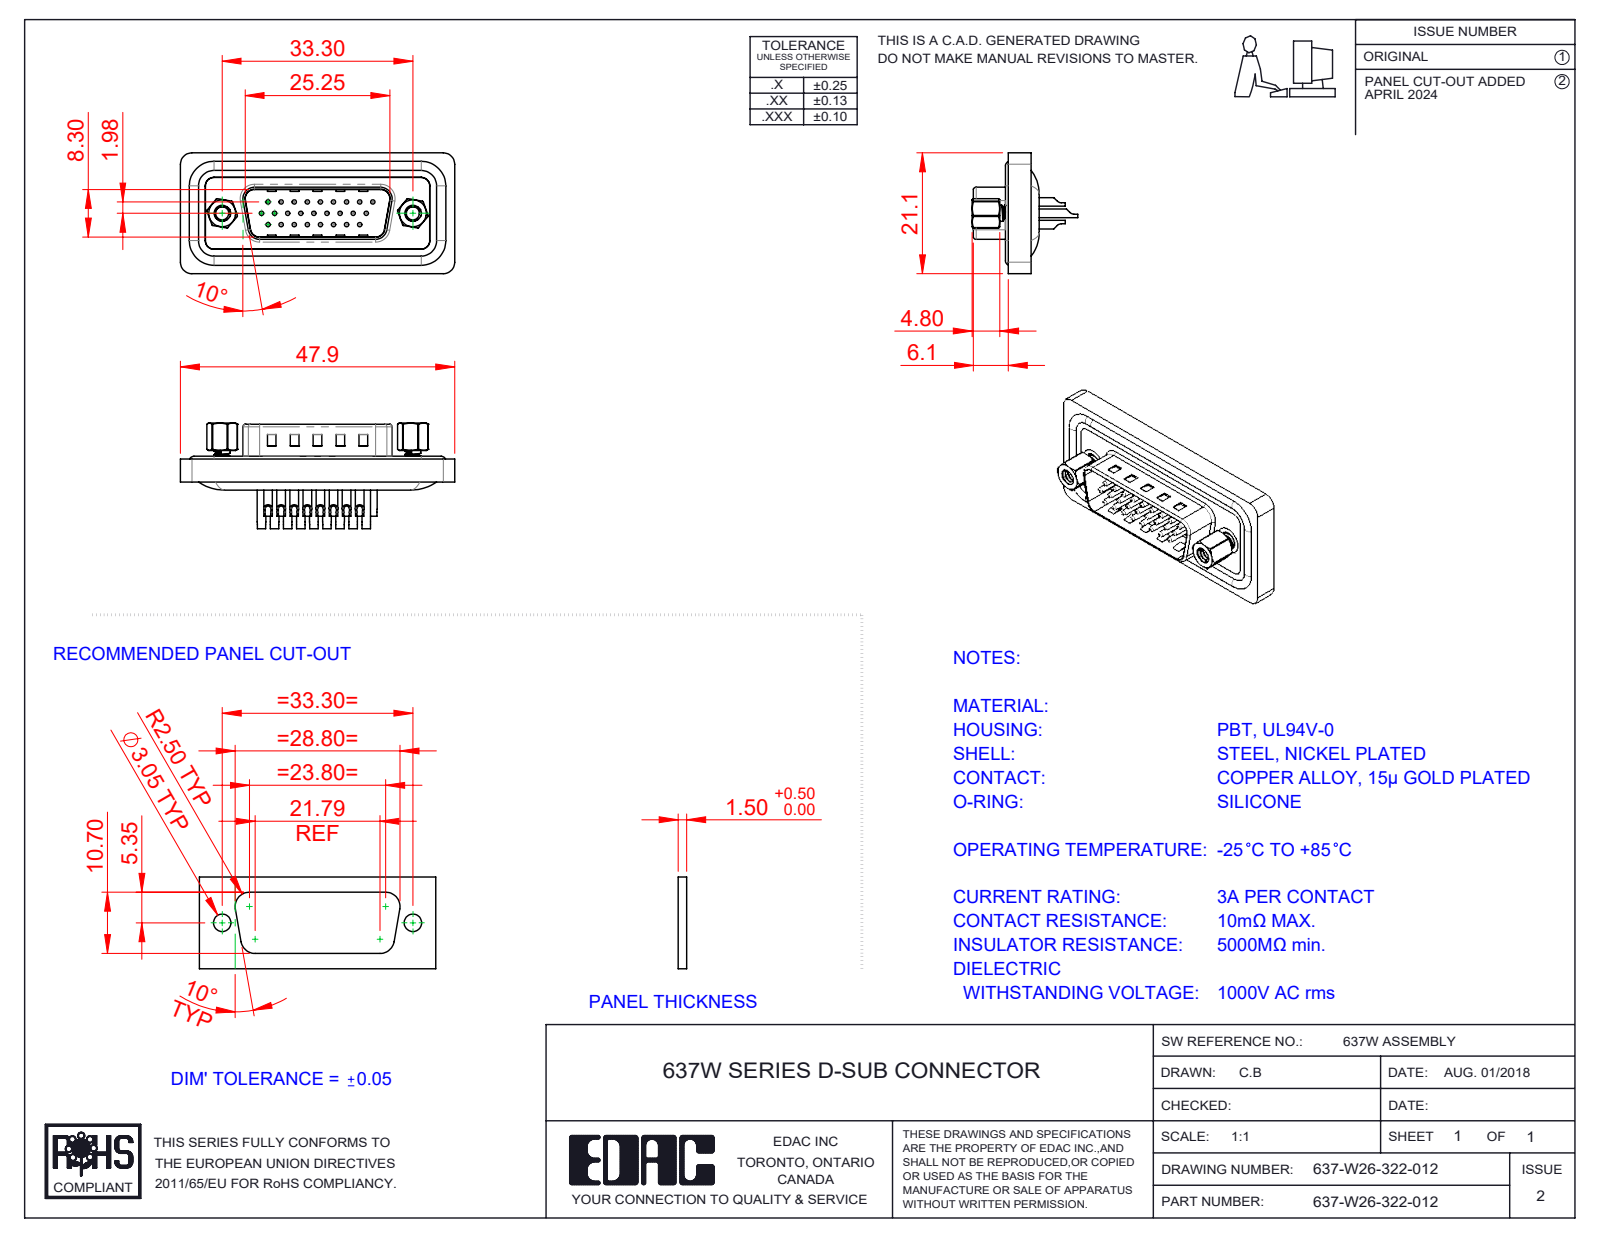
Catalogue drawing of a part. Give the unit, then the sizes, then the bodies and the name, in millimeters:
Units: millimetres
Overall size (bounding box): 47.89 × 21.1 × 18.45
Round holes (diameter × count): ⌀0.75 ×26, ⌀1 ×26, ⌀1.5 ×26, ⌀1.6 ×26, ⌀2 ×26, ⌀2.26 ×2, ⌀2.29 ×2, ⌀4 ×2, ⌀4.8 ×2, ⌀5 ×2
Round bosses / shafts (diameter × count): ⌀1.5 ×26, ⌀1.6 ×4, ⌀4.9 ×2, ⌀2.79 ×2, ⌀5 ×1
Partial cylindrical surfaces — rounded edges, fillets, slot ends (radius × count): R2 ×16, R1.5 ×14, R0.5 ×8, R2.7 ×6, R0.9 ×4, R1.6 ×4, R4.3 ×4, R1 ×3
Main face-to-face distances: 0.4, 1.6, 1.1, 2.9, 2.5, 0.5, 4, 5.65, 15.45, 3.4
Hole centre spacings: 3.96, 2.28, 4.57, 6.05, 2.29, 8.24, 6.86, 10.48
Volume: 4 968 mm³ · Surface area: 9 096 mm²
Bodies: 34 solids, 1498 faces (407 planar, 684 cylindrical, 407 other)
Part name (STEP PRODUCT): 637W Contact Row 1_22; 637W Shell_26 Contacts; 637-W26-322-012; 637W Contact Row 2_22 (+5 more)
STEP written by: SolidWorks 2023 (CONFIG_CONTROL_DESIGN)
